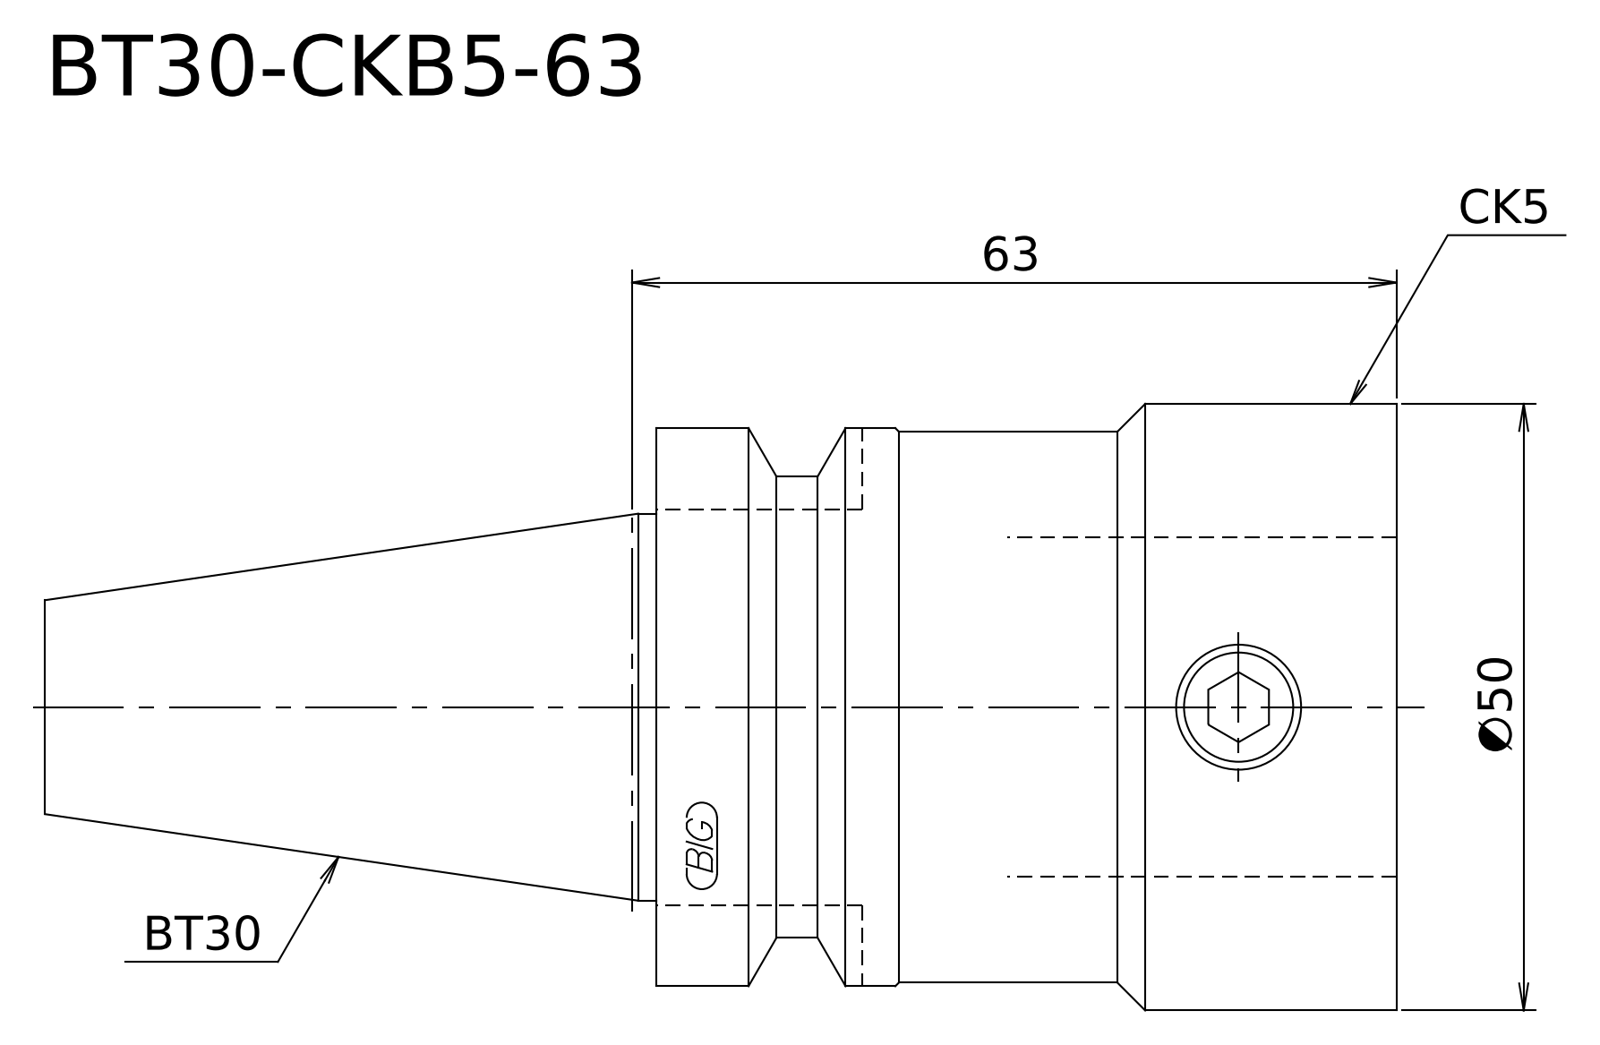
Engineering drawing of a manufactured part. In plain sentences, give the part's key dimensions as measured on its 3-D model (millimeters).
Its 3-D file was written by "Kubotek KeyCreator V8.5.1 (14335) (CONFIG_CONTROL_DESIGN)". It is 1 solid with 14 faces: 3 planar, 6 cylindrical and 5 other. Overall it measures 111.4 by 50 by 50 millimeters. Its volume is 129 488 cubic millimeters and its surface area 16 746 square millimeters. Round bosses or shafts: 1 of diameter 50, 1 of diameter 46, 1 of diameter 45.4, 1 of diameter 38, 1 of diameter 31.9. The main face-to-face distances are 61, 111.4, 50.4.
